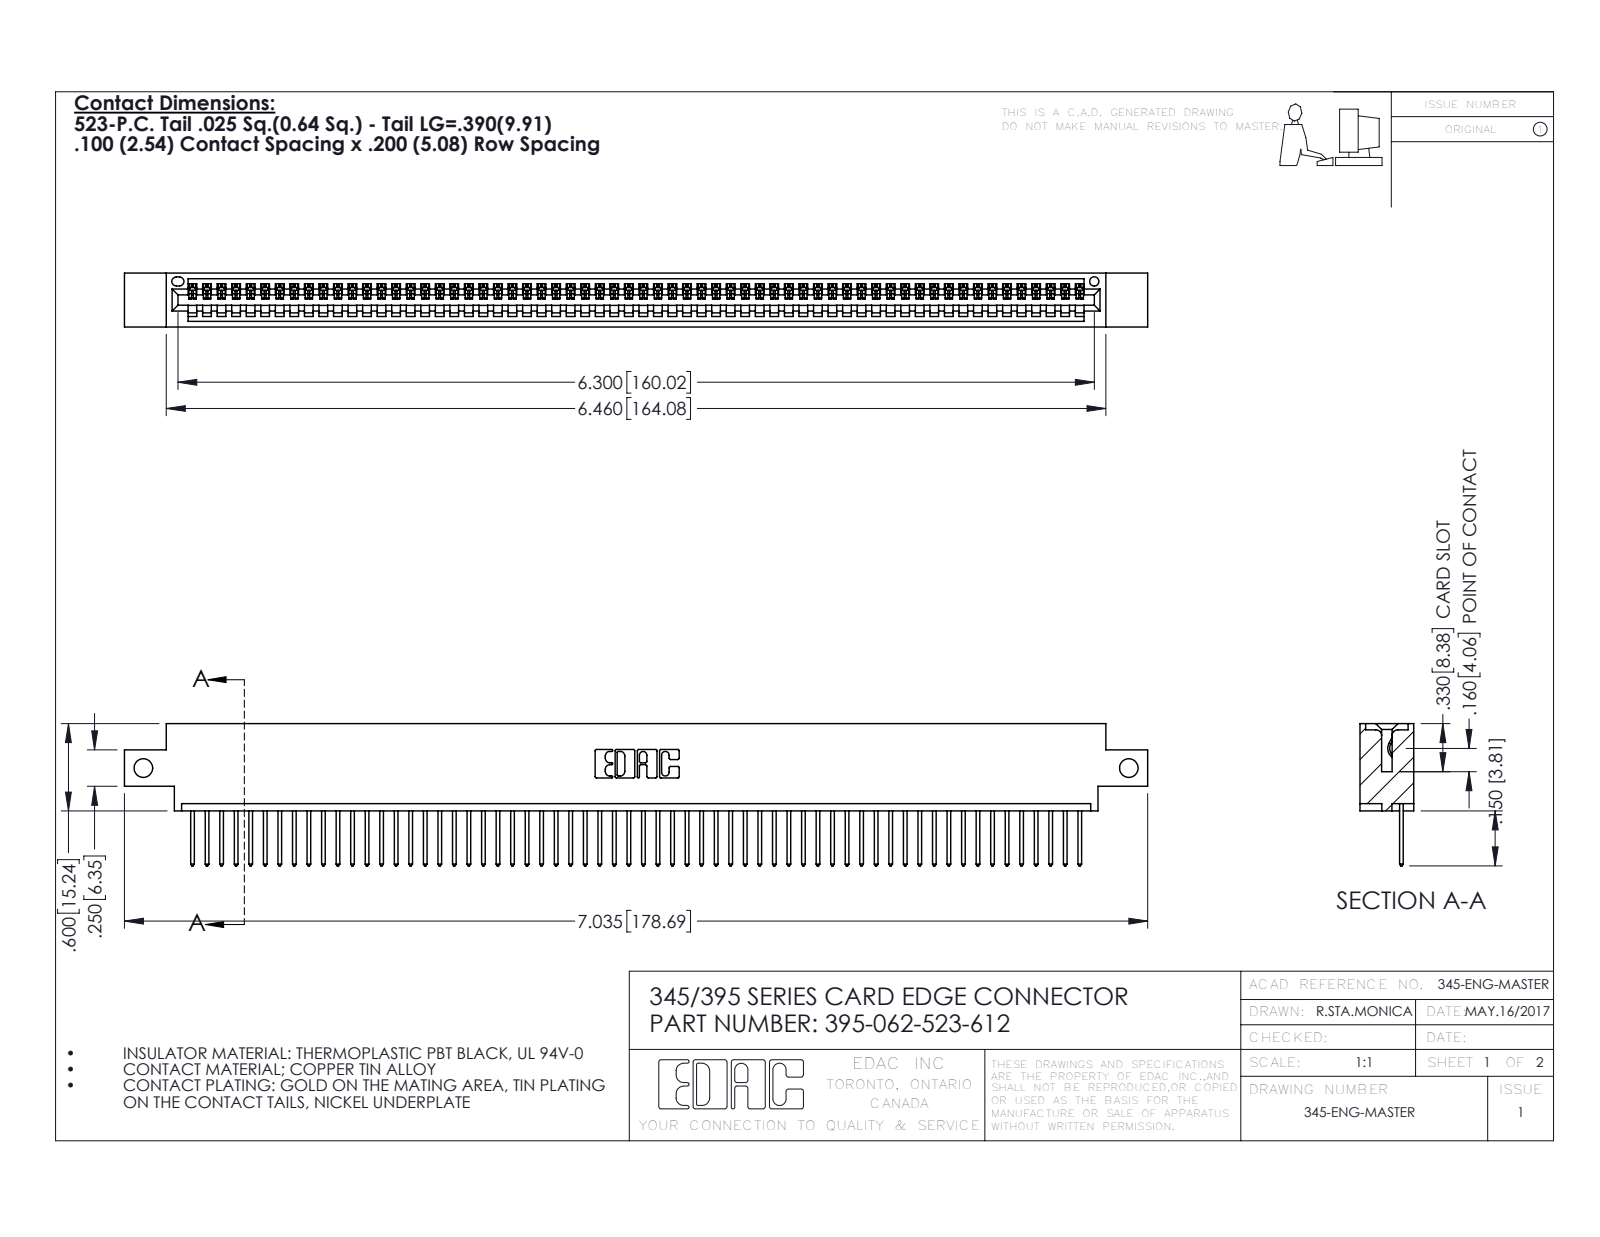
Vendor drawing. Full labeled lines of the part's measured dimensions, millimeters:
Part name (STEP PRODUCT): 345 Part_0.170 Offset - Side Mount; 345-292-001_345-293-123; 395-062-523-612
STEP written by: SolidWorks 2016 (CONFIG_CONTROL_DESIGN)
Units: millimetres
Bodies: 63 solids, 3726 faces (2564 planar, 1162 cylindrical, 0 other)
Overall size (bounding box): 178.7 × 24.8 × 9.4
Volume: 16 910 mm³ · Surface area: 22 800 mm²
Round holes (diameter × count): ⌀3.3 ×2, ⌀1.6 ×1
Partial cylindrical surfaces — rounded edges, fillets, slot ends (radius × count): R0.2 ×124, R0.3 ×124, R0.3 ×22, R0.2 ×6, R0.8 ×6, R0.7 ×3, R0.8 ×2, R1 ×2
Main face-to-face distances: 7.6, 1.8, 9.4, 2.5, 6.9, 0.6, 5.1, 5.7, 4.4, 3.8
Hole centre spacings: 172.1
